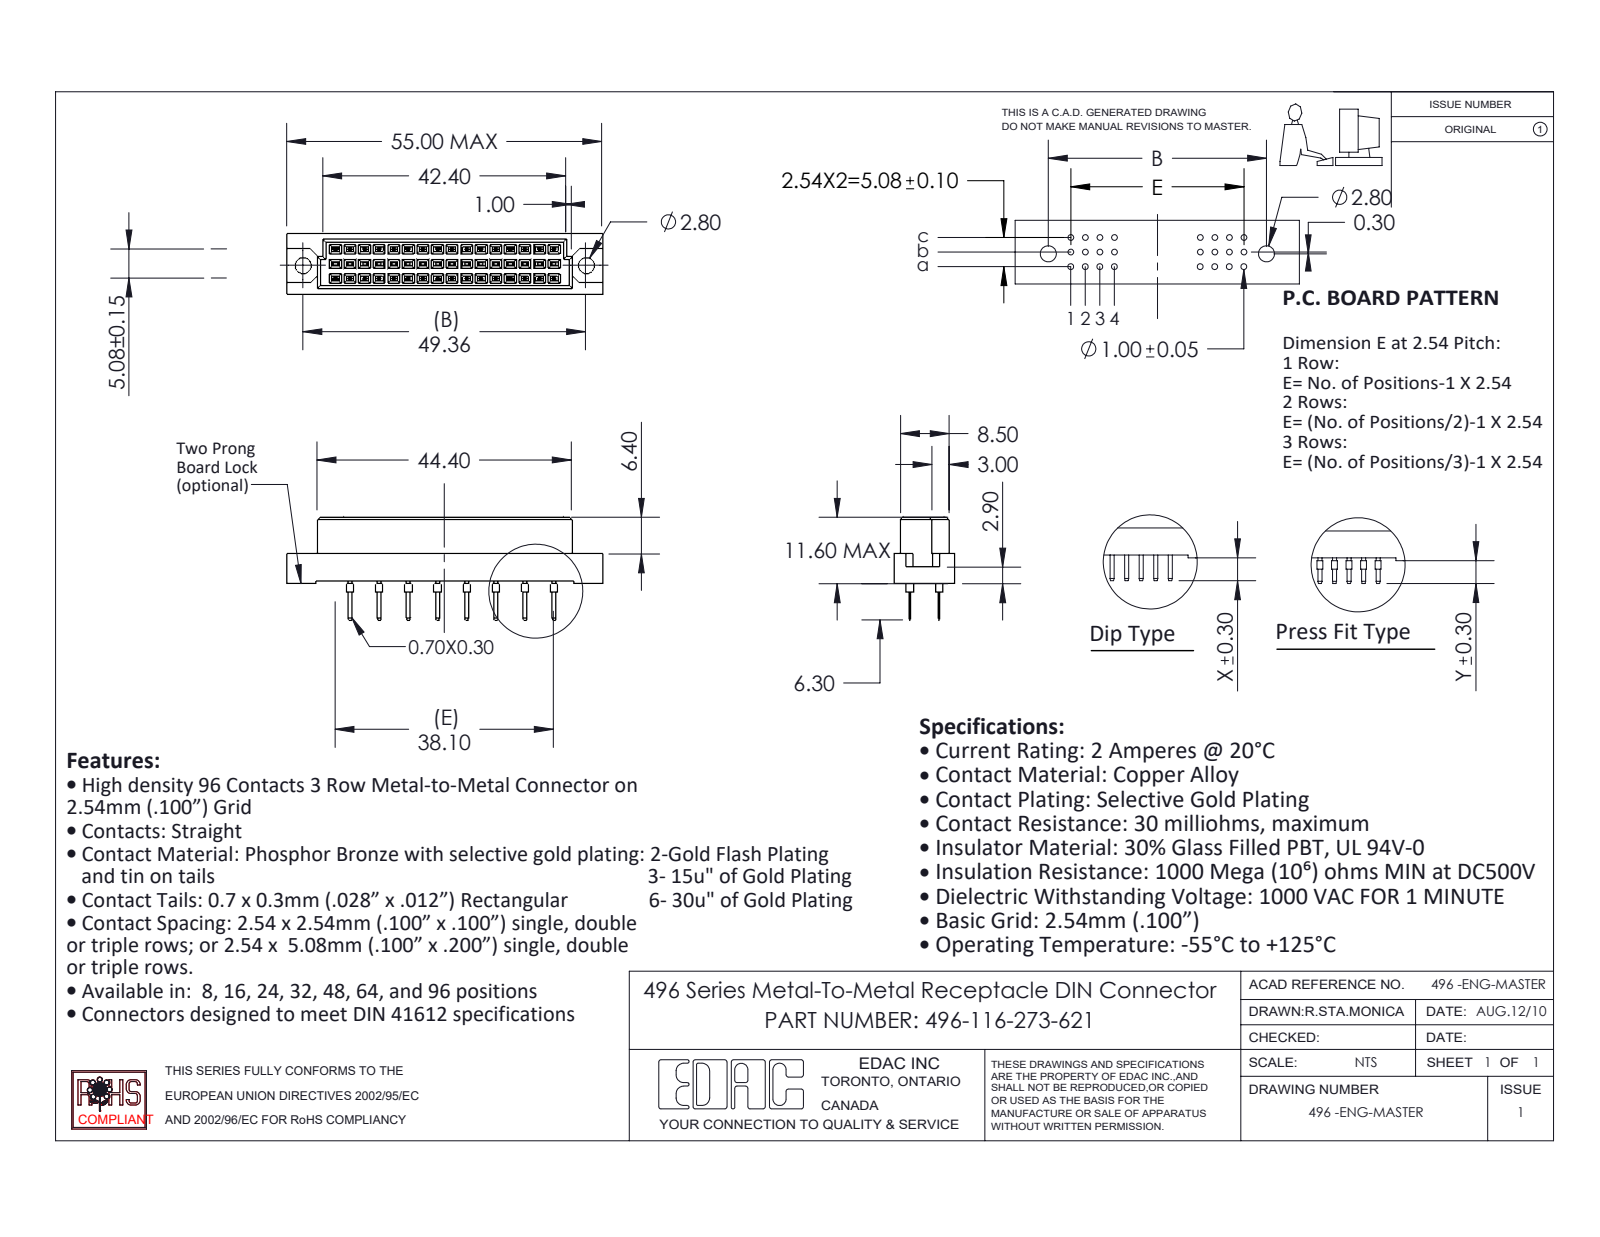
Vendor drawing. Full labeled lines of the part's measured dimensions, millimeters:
Part name (STEP PRODUCT): 496-290_73; 496 Part_48; 496-116-273-621
STEP written by: SolidWorks 2020 (CONFIG_CONTROL_DESIGN)
Units: millimetres
Bodies: 17 solids, 954 faces (918 planar, 36 cylindrical, 0 other)
Overall size (bounding box): 55 × 17.9 × 10.6
Volume: 4 639 mm³ · Surface area: 4 607 mm²
Round holes (diameter × count): ⌀2.8 ×2
Round bosses / shafts (diameter × count): ⌀1 ×16
Main face-to-face distances: 2.54, 5.08, 1.05, 9.55, 0.81, 0.56, 10.6, 0.55, 3.35, 1.73
Hole centre spacings: 49.36
